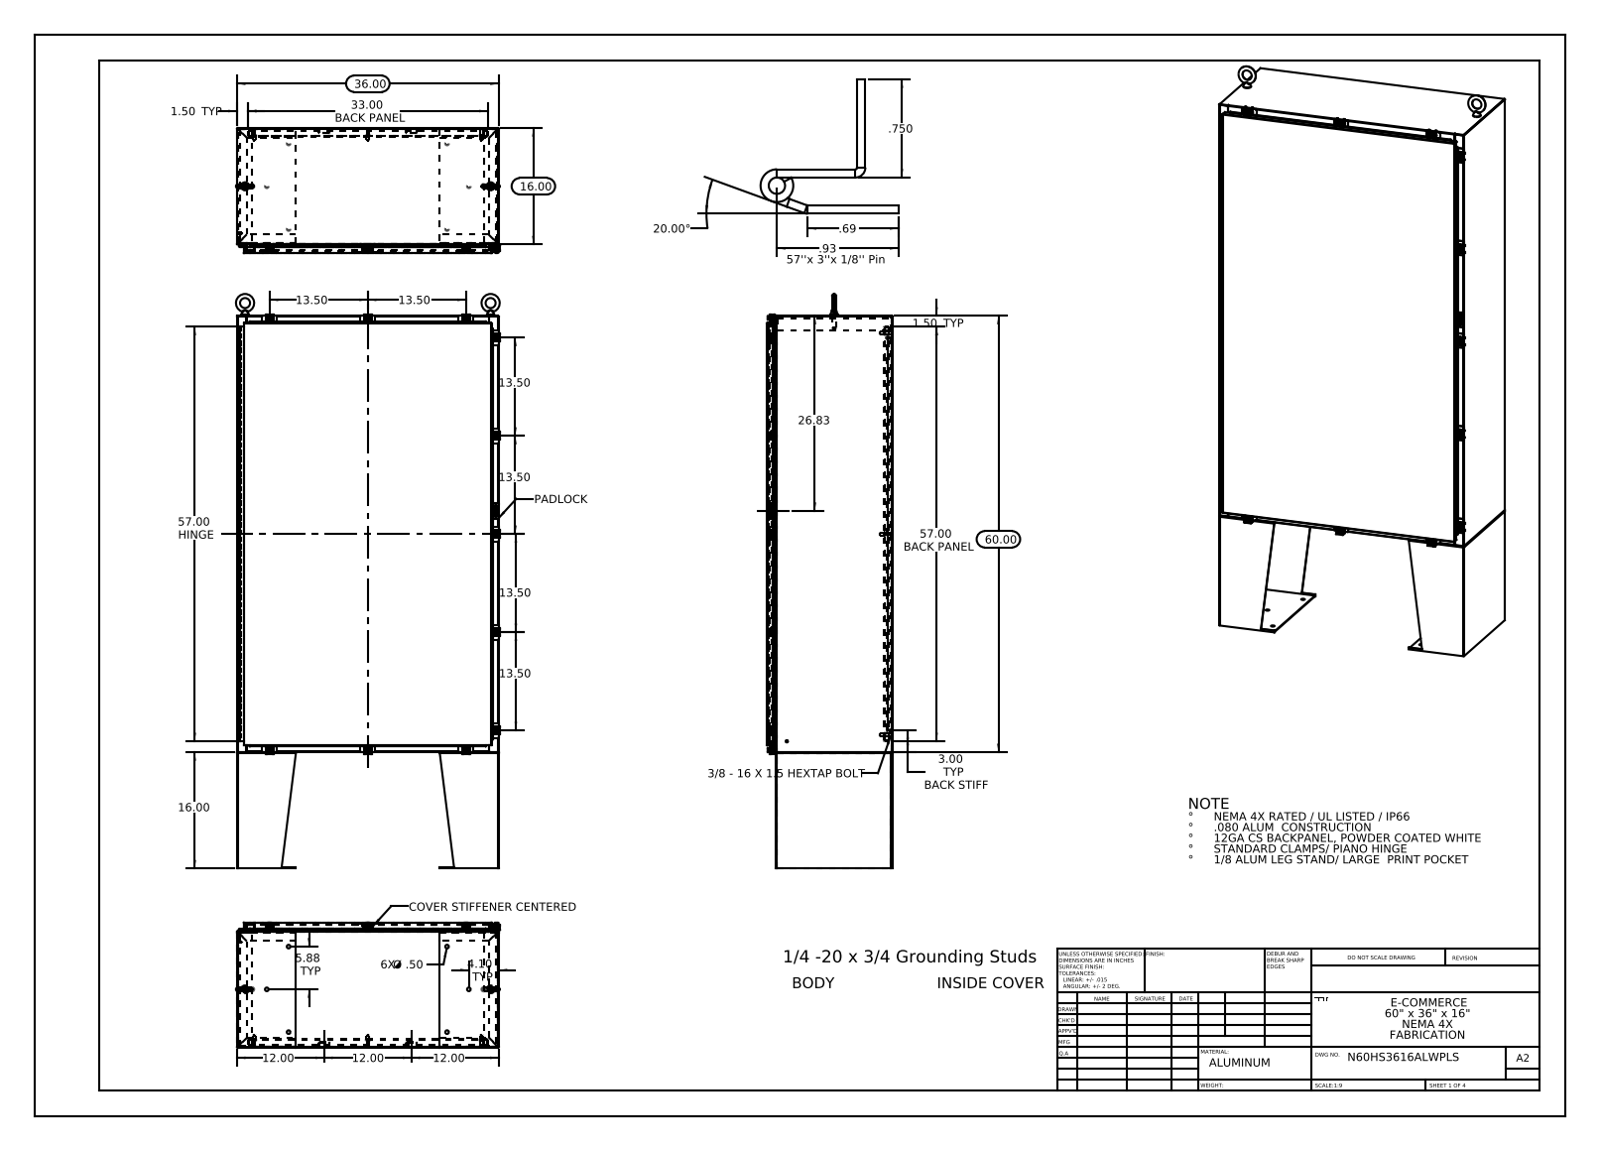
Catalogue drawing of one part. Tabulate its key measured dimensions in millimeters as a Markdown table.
| quantity | value |
| --- | --- |
| part name | N60HS3616SSWPLS 22104005_DEFAULT; N60HS3616SSWPLS Backpanel; N60HS3616SSWPLS SD-LSK-Stand; N60HS3616SSWPLS SD-LSK - Base (+8 more) |
| STEP written by | SolidWorks 2013 (CONFIG_CONTROL_DESIGN) |
| units | millimeters |
| bodies | 93 solids, 3674 faces (1872 planar, 1518 cylindrical, 284 other) |
| overall size | 2006.6 × 923.2 × 436.9 |
| volume | 16 450 000 mm³ |
| surface area | 15 620 000 mm² |
| round holes (diameter × count) | 12.7 × 14, 5.4 × 11, 6.6 × 11, 6.4 × 8, 19.1 × 4, 3.2 × 2, 3.2 × 1 |
| round bosses / shafts (diameter × count) | 6.4 × 12, 12.7 × 11, 10.1 × 11, 15.9 × 10, 9.5 × 8, 8.4 × 8, 4 × 8, 3.6 × 8 |
| partial cylindrical surfaces (radius × count) | 1.5 × 50, 0.3 × 39, 2.2 × 33, 3 × 22, 3.6 × 22, 1.3 × 17, 2 × 16, 2.3 × 16 |
| main face-to-face distances | 1.9, 435, 2.6, 433.1, 27.3, 436.9, 912.5, 409.6, 25.4, 407.7 |
| hole center spacings | 342.9, 347, 685.8, 56.5, 213.2, 647.2, 701.7, 721.3 |
